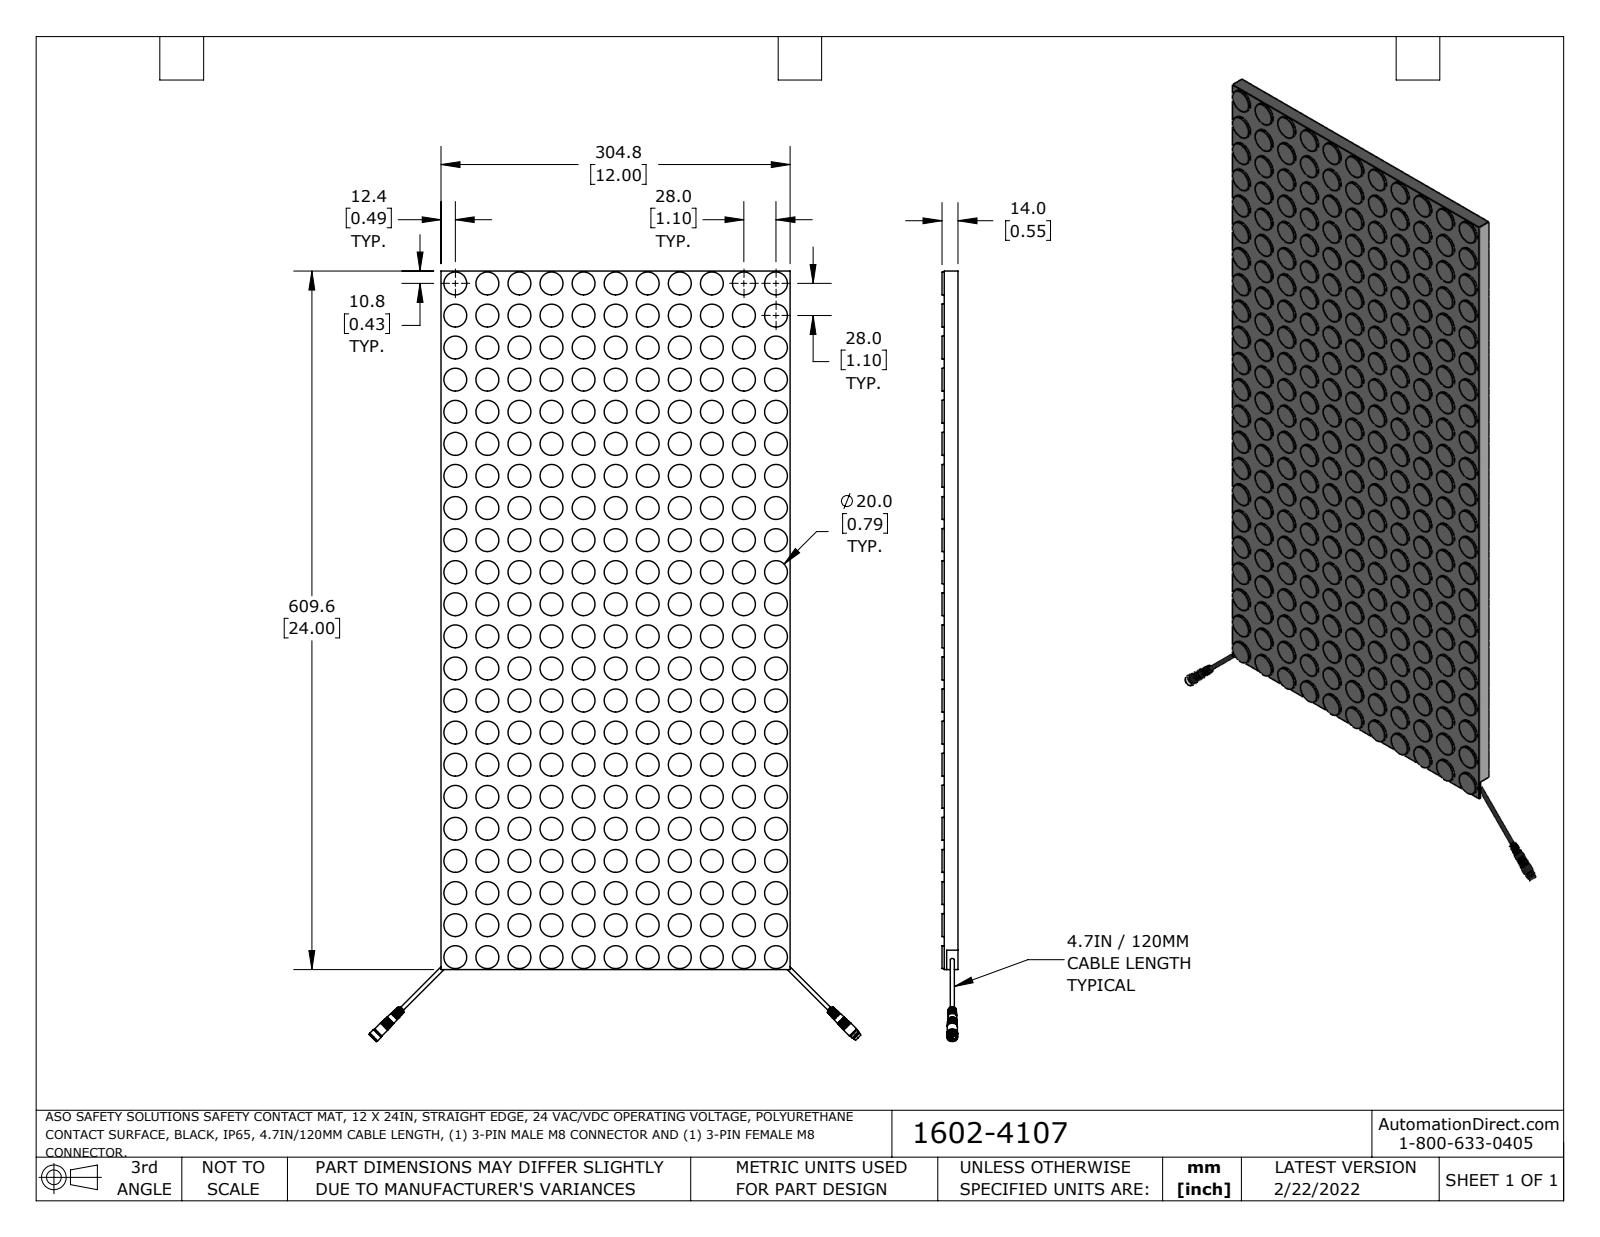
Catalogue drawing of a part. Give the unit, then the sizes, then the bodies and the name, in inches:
Units: inches
Overall size (bounding box): 26.474 × 16.904 × 0.551
Round holes (diameter × count): ⌀0.063 ×3, ⌀0.134 ×2, ⌀0.228 ×1, ⌀0.232 ×1, ⌀0.272 ×1, ⌀0.283 ×1
Round bosses / shafts (diameter × count): ⌀0.787 ×242, ⌀0.047 ×24, ⌀0.031 ×8, ⌀0.039 ×3, ⌀0.346 ×2, ⌀0.138 ×2, ⌀0.378 ×1, ⌀0.354 ×1
Main face-to-face distances: 0.472, 0.079, 0.551, 12, 24, 0.087, 0.394, 0.157, 0.173, 0.039
Hole centre spacings: 0.069, 0.097, 0.137
Volume: 145.4 in³ · Surface area: 665.3 in²
Bodies: 20 solids, 1110 faces (370 planar, 602 cylindrical, 138 other)
Part name (STEP PRODUCT): 1602-4107_Default
STEP written by: SolidWorks 2021 (CONFIG_CONTROL_DESIGN)
